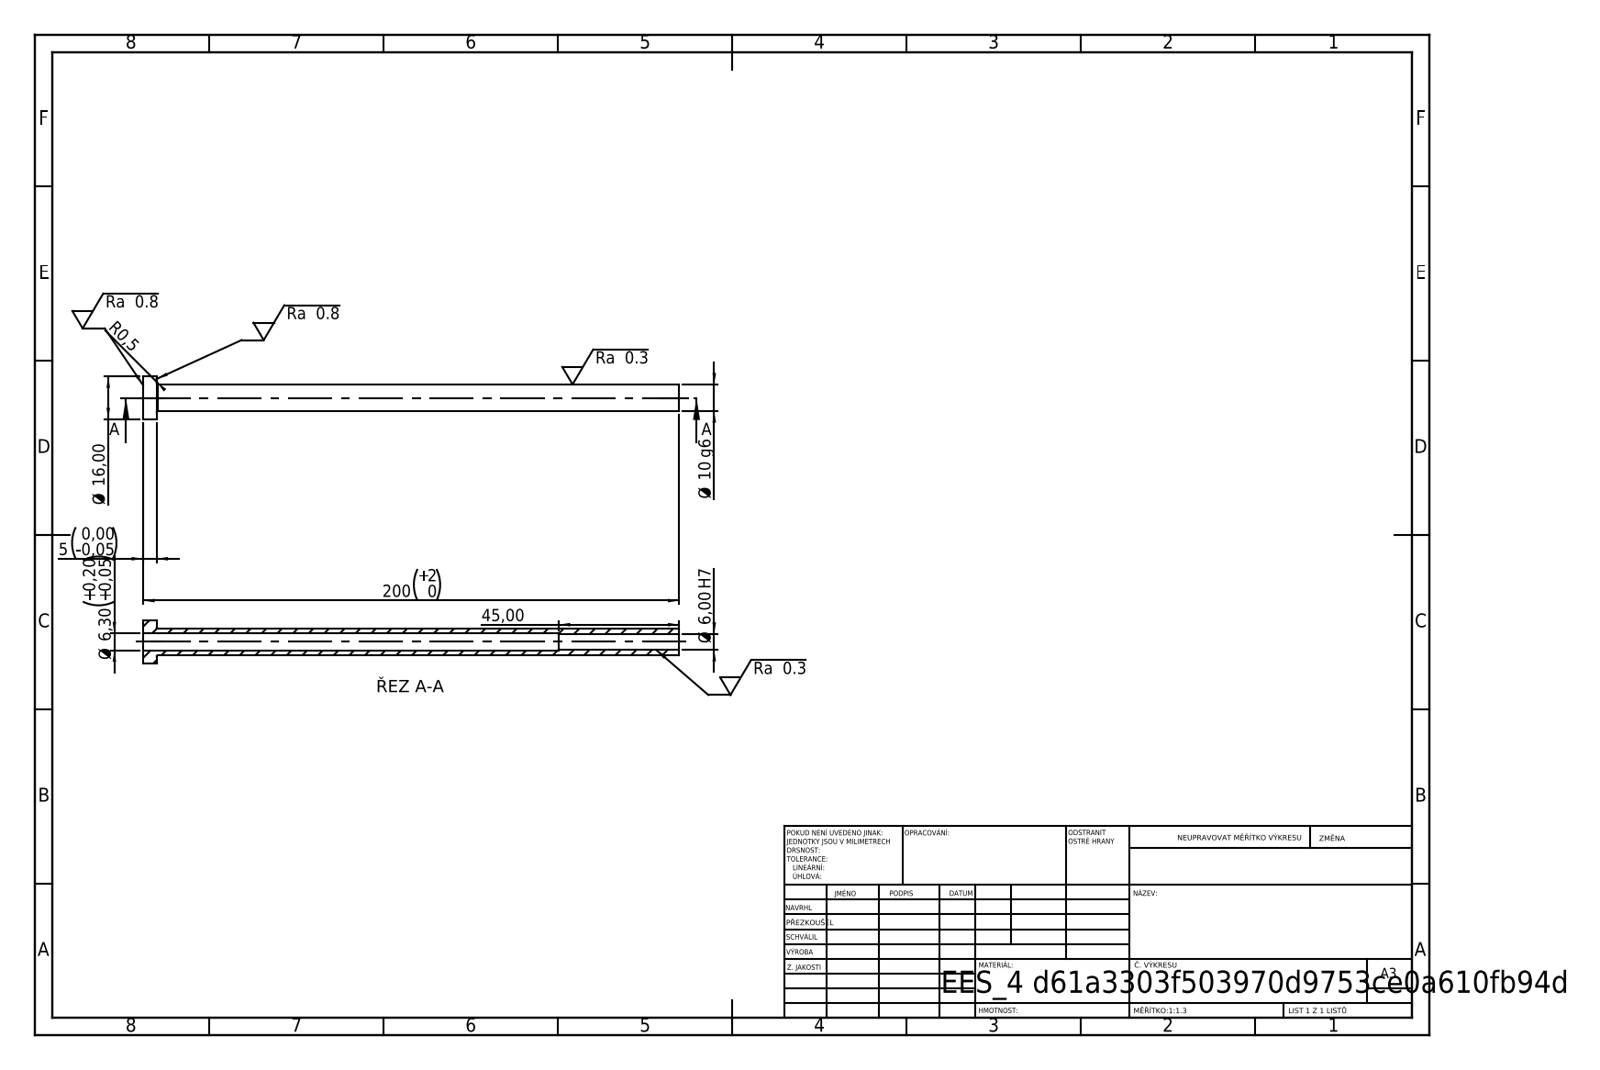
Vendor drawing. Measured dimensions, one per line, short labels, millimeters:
written by: SolidWorks 2019 (CONFIG_CONTROL_DESIGN)
unit: mm
bodies: 1 solid, 14 faces (4 planar, 8 cylindrical, 2 other)
size: 200 × 16 × 16
volume: 10 218 mm³; area: 10 632 mm²
holes: 1× ⌀6, 1× ⌀6.3
bosses: 1× ⌀16, 1× ⌀10
face distances: 5, 200, 195, 155, 150, 45
